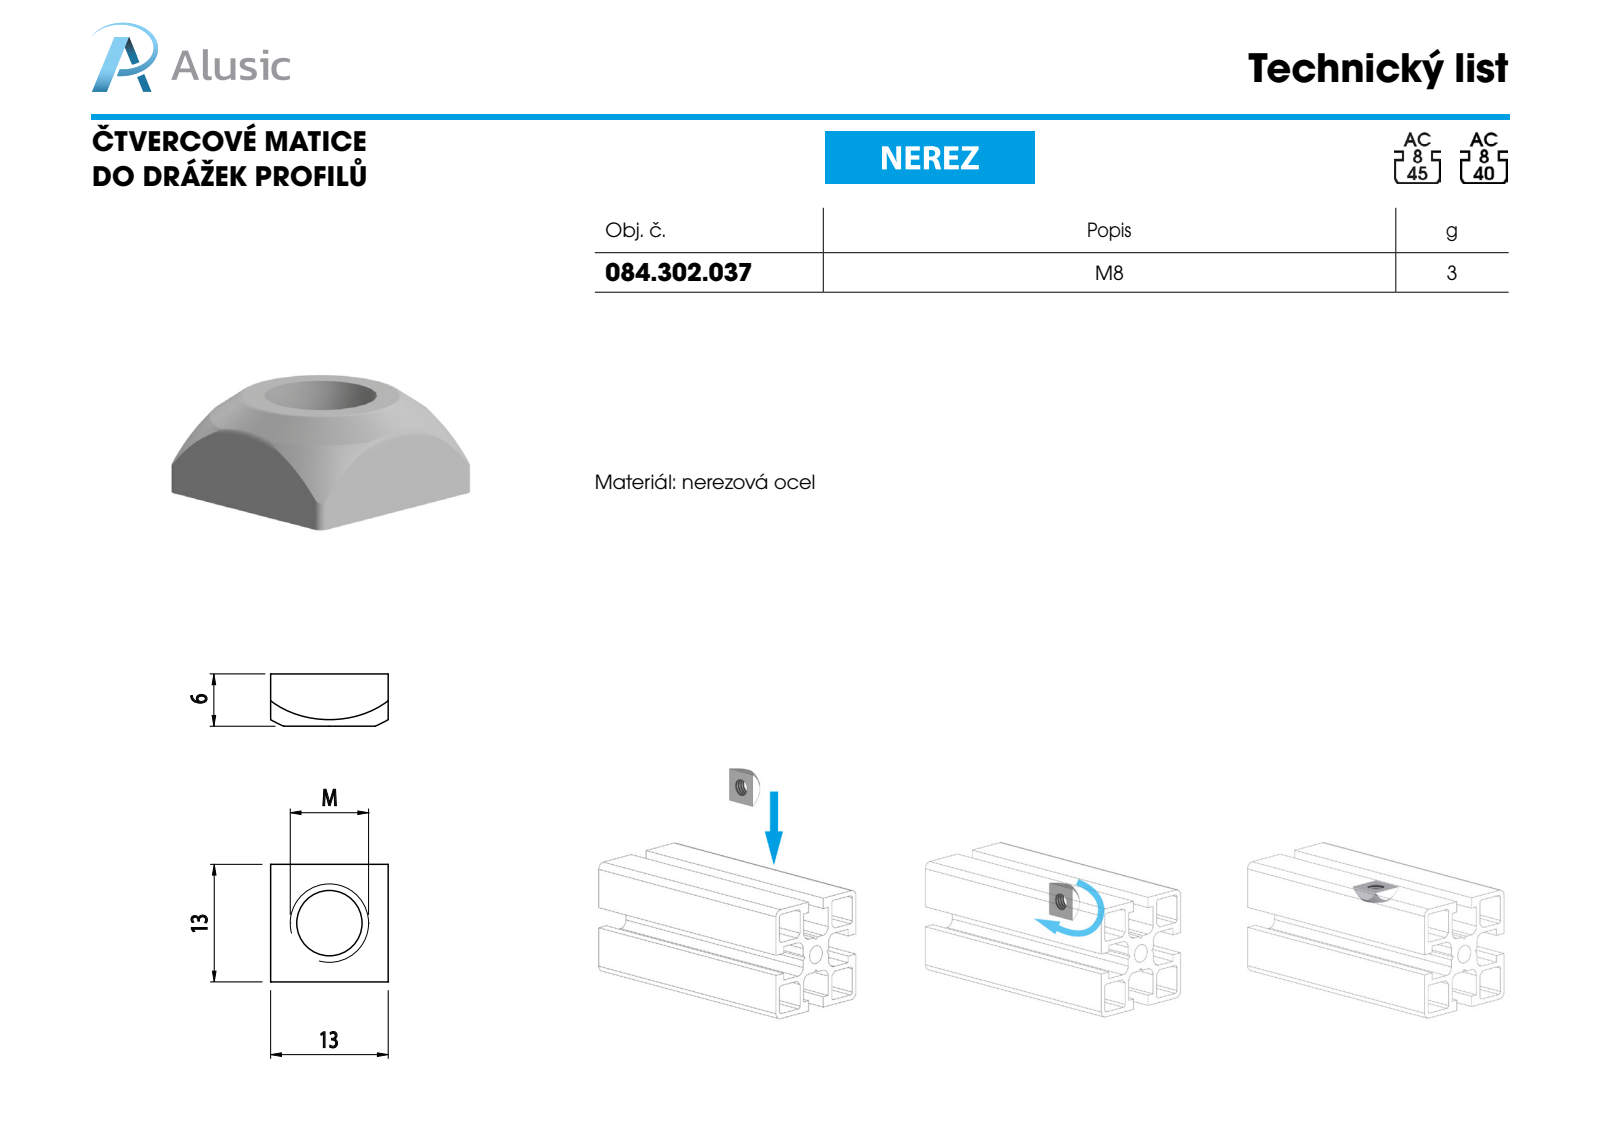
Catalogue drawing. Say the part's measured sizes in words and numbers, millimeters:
The part is named "084.302.037". Its 3-D file was written by "SolidWorks 2016 (CONFIG_CONTROL_DESIGN)". It is 1 solid with 14 faces: 6 planar, 2 cylindrical and 6 other. Overall it measures 13 by 13 by 6 millimeters. Its volume is 821 cubic millimeters and its surface area 616 square millimeters. Round holes: 1 of diameter 4.2. The main face-to-face distances are 13, 6.
